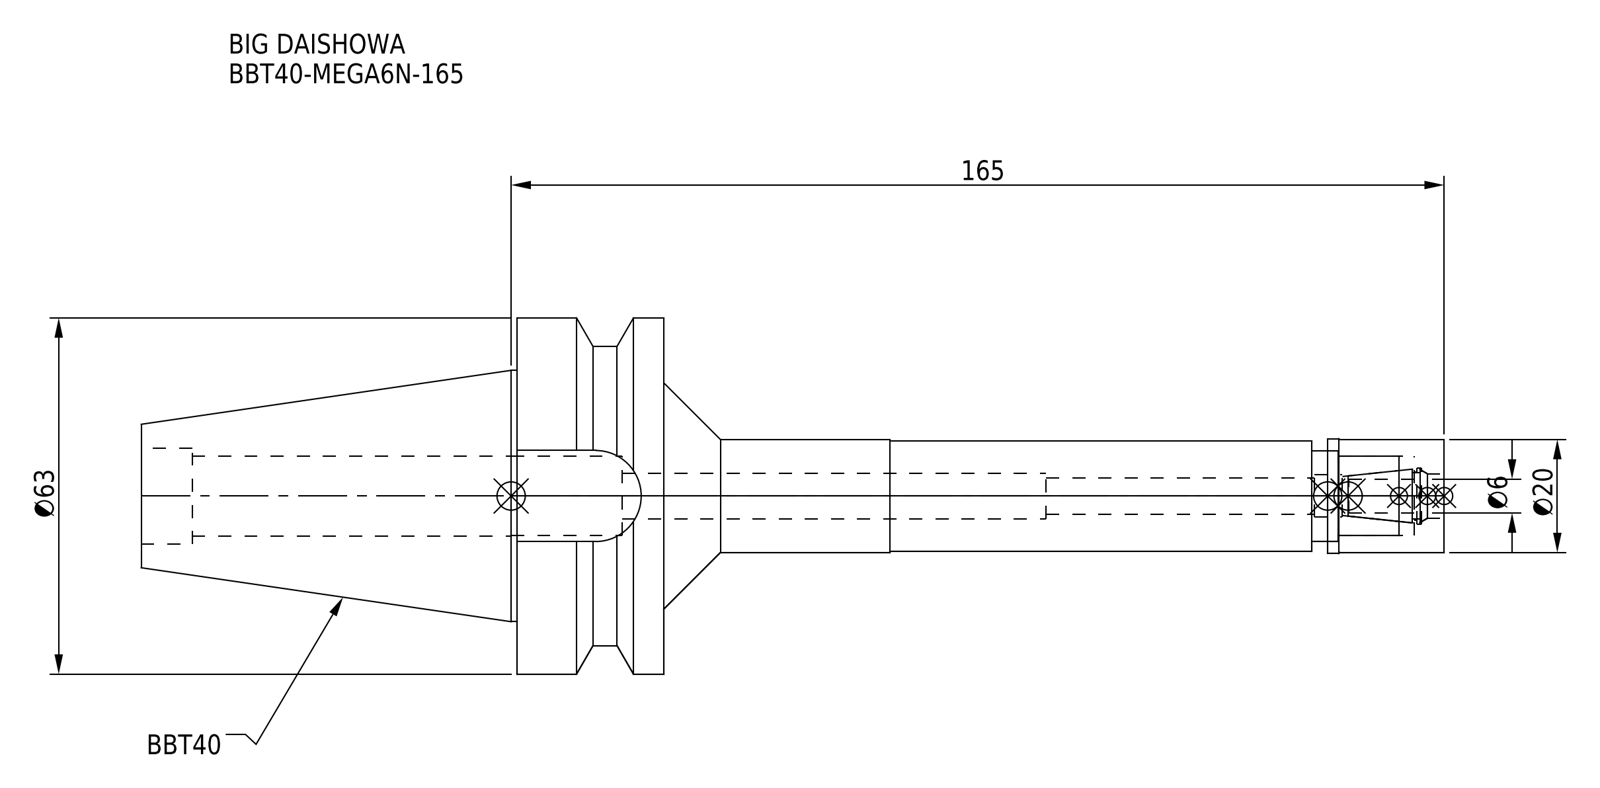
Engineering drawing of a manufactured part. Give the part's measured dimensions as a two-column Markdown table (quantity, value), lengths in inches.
| quantity | value |
| --- | --- |
| part name | MGN6_1.stp; BBT40-MEGA6N-165_1.stp; DXF_TEMP_ASSY_ASM_4_ASM.stp; BBT40-MEGA6N-165 (+3 more) |
| STEP written by | SolidWorks 2019 (CONFIG_CONTROL_DESIGN) |
| units | inches |
| bodies | 2 solids, 83 faces (25 planar, 44 cylindrical, 14 other) |
| overall size | 9.071 × 2.48 × 2.48 |
| volume | 9.822 in³ |
| surface area | 55.87 in² |
| round holes (diameter × count) | 0.252 × 1, 0.295 × 1, 0.311 × 1, 0.315 × 1, 0.335 × 1, 0.394 × 1, 0.551 × 1, 0.559 × 1, 0.63 × 1, 0.669 × 1 |
| round bosses / shafts (diameter × count) | 2.48 × 1, 2.087 × 1, 1.75 × 1, 0.799 × 1, 0.787 × 1, 0.768 × 1 |
| partial cylindrical surfaces (radius × count) | 0.317 × 1 |
| main face-to-face distances | 1.024, 1.772, 2.614, 3.638, 5.433, 6.457, 9.071, 0.634, 0.732, 0.811 |
